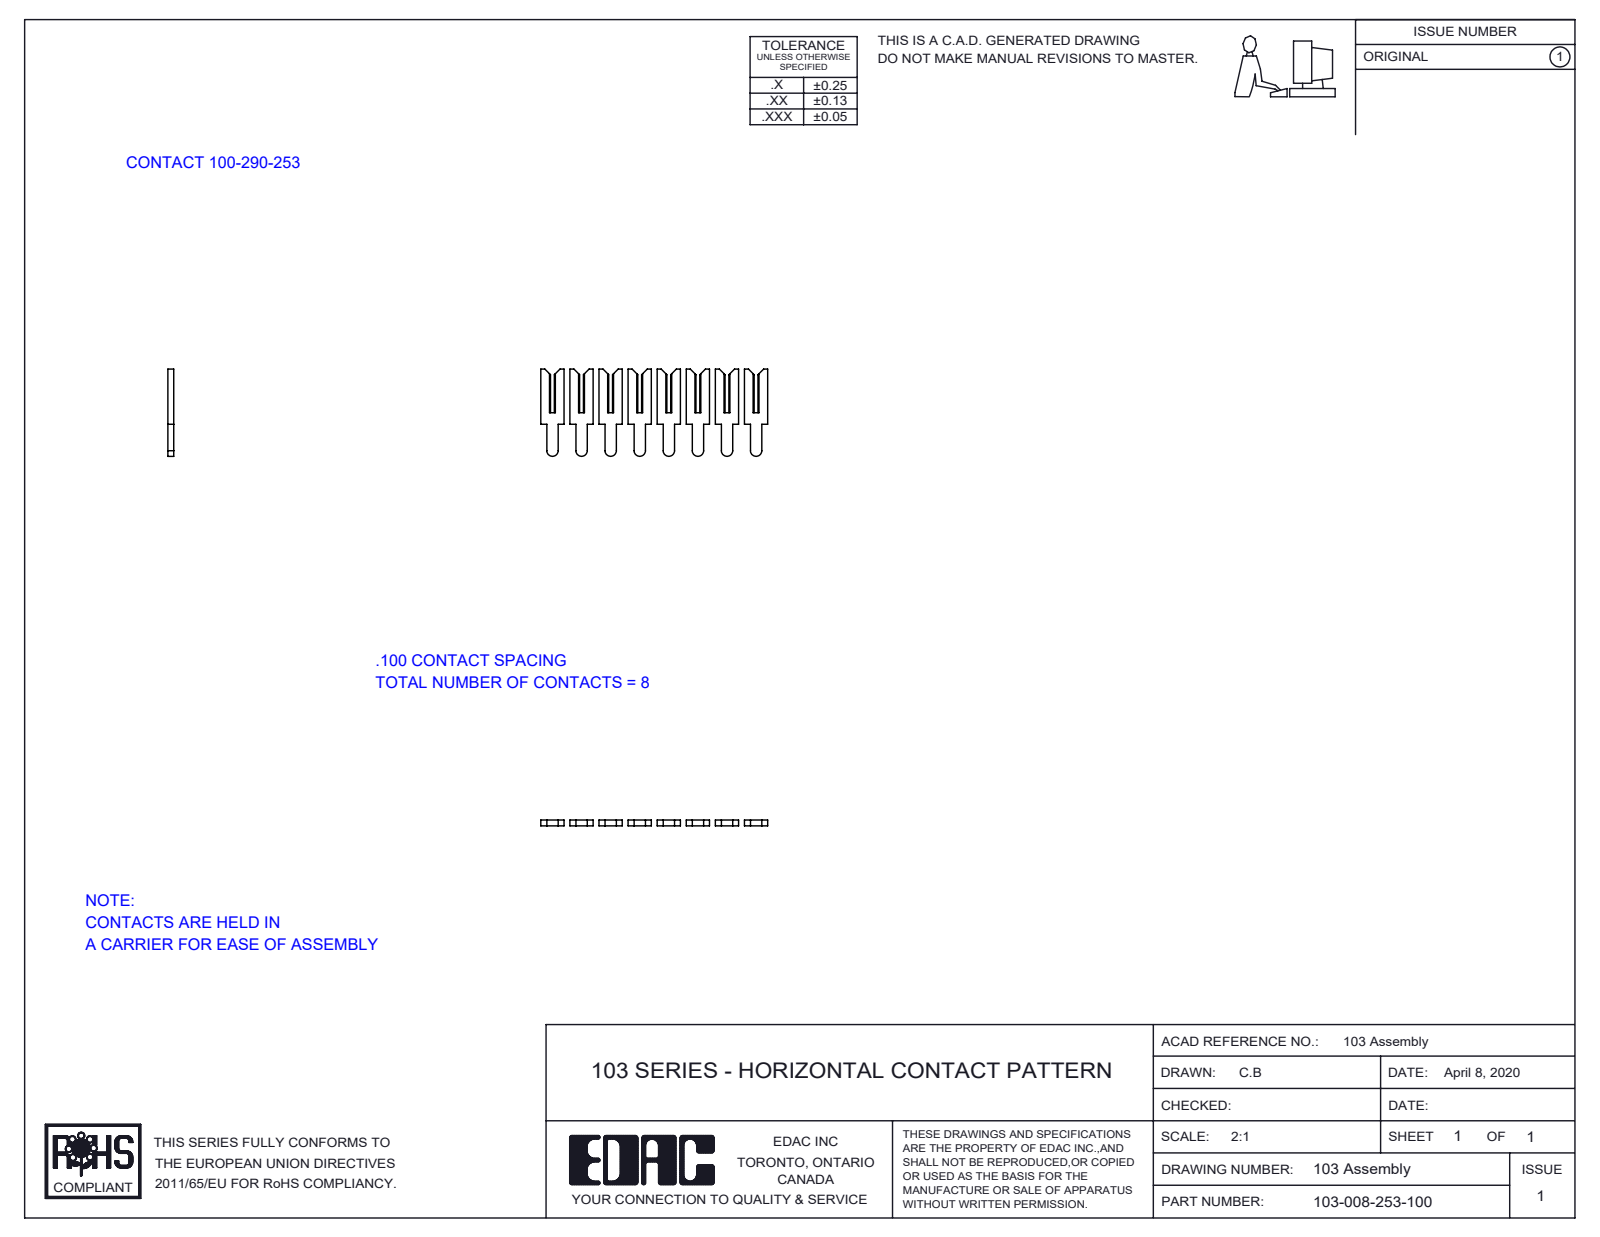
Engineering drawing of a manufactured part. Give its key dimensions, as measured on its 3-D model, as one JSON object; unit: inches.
{"part_name": "103-008-253-100; 100-290-001_100-290-253", "step_written_by": "SolidWorks 2016 (CONFIG_CONTROL_DESIGN)", "units": "inches", "bodies": {"solids": 8, "faces": 160, "planar": 152, "cylindrical": 8, "other": 0}, "overall_size": [0.78, 0.3, 0.02], "volume_in3": 0.003, "surface_area_in2": 0.427, "partial_cylinders_radius": [[0.019, 8]], "face_to_face_distances": [0.02, 0.1, 0.2, 0.3, 0.4, 0.08, 0.18, 0.5, 0.28, 0.12]}
